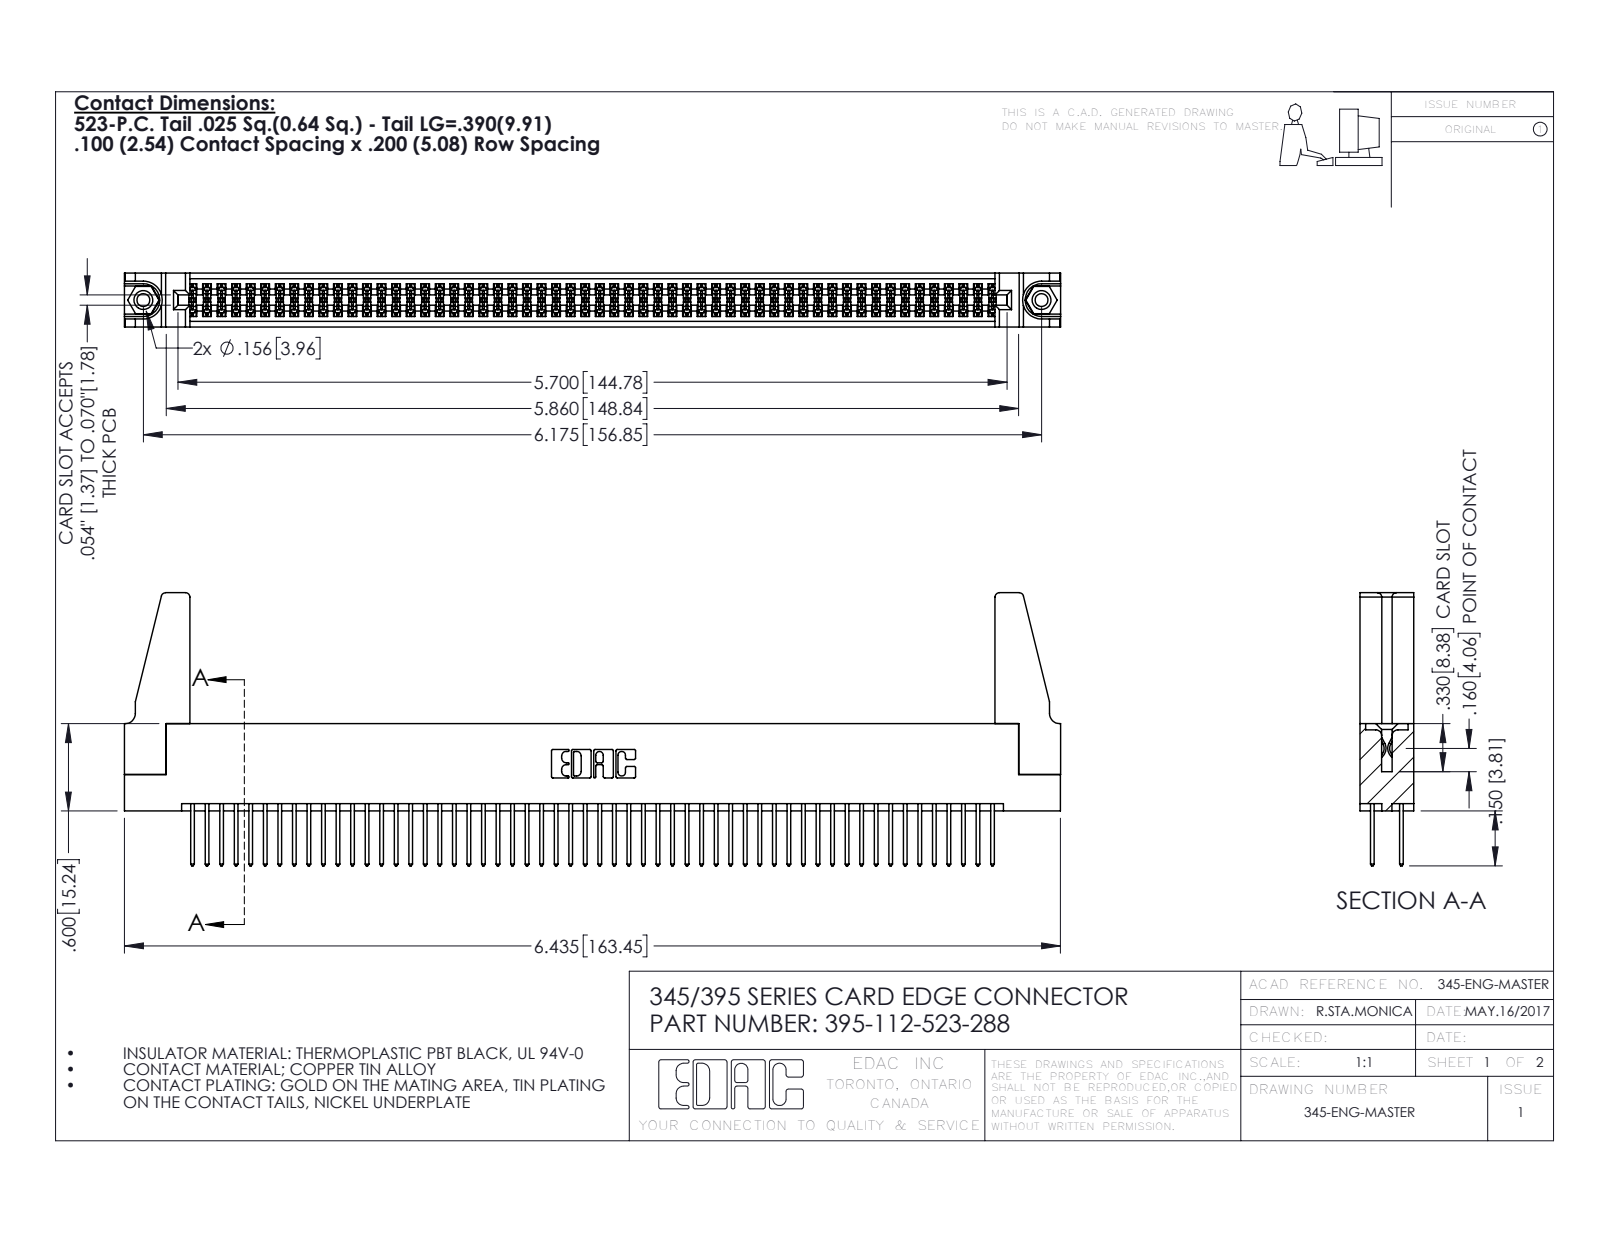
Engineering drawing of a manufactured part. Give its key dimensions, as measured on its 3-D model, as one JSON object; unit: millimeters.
{"part_name": "345-250-001_345-250-001-102; 345 Part_Flush Mounting Lugs - 0.156 Dia-TH; 345-292-001_345-293-123; 345-220-078_345-220-088 (+1 more)", "step_written_by": "SolidWorks 2016 (CONFIG_CONTROL_DESIGN)", "units": "millimeters", "bodies": {"solids": 117, "faces": 5850, "planar": 3848, "cylindrical": 1986, "other": 16}, "overall_size": [163.5, 47.7, 9.4], "volume_mm3": 19480, "surface_area_mm2": 28430, "round_holes": [[2.3, 2], [3.2, 2], [4, 2], [1.6, 1]], "round_bosses_or_shafts": [[3.9, 2]], "partial_cylinders_radius": [[0.2, 168], [0.3, 112], [0.3, 22], [0.8, 8], [0.2, 6], [0.8, 6], [0.7, 3], [0.4, 2]], "face_to_face_distances": [1.8, 7.6, 5.1, 9.4, 2.5, 6.9, 0.6, 5.7, 4.4, 3.8], "hole_center_spacings": [6.9, 150.9, 156.8]}
